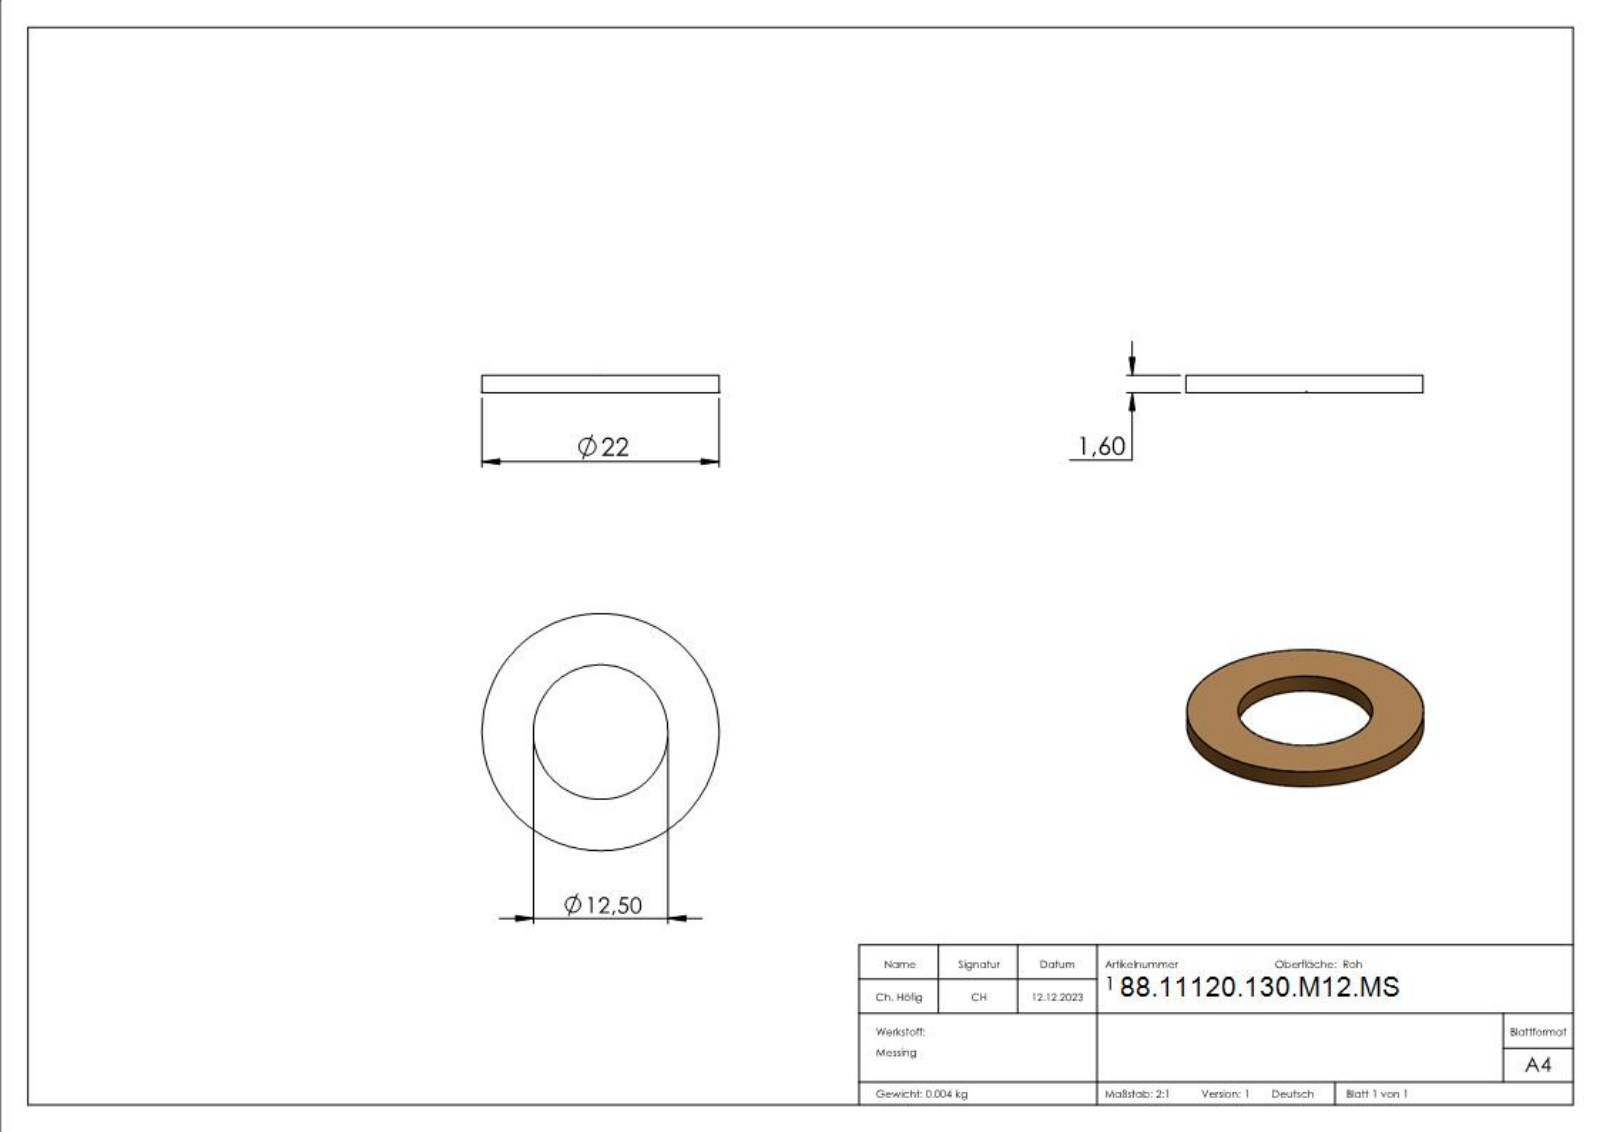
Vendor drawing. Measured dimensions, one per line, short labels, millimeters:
name: 120-130-M12-MS
written by: SolidWorks 2015 (CONFIG_CONTROL_DESIGN)
unit: mm
bodies: 1 solid, 267 faces (156 planar, 4 cylindrical, 107 other)
size: 22 × 22 × 1.5
volume: 386 mm³; area: 680 mm²
holes: 1× ⌀12.5
bosses: 1× ⌀22
face distances: 1.5, 1.4, 0.77, 0.73, 0.86, 16.37, 17.1, 18.17, 1.8, 1.07
